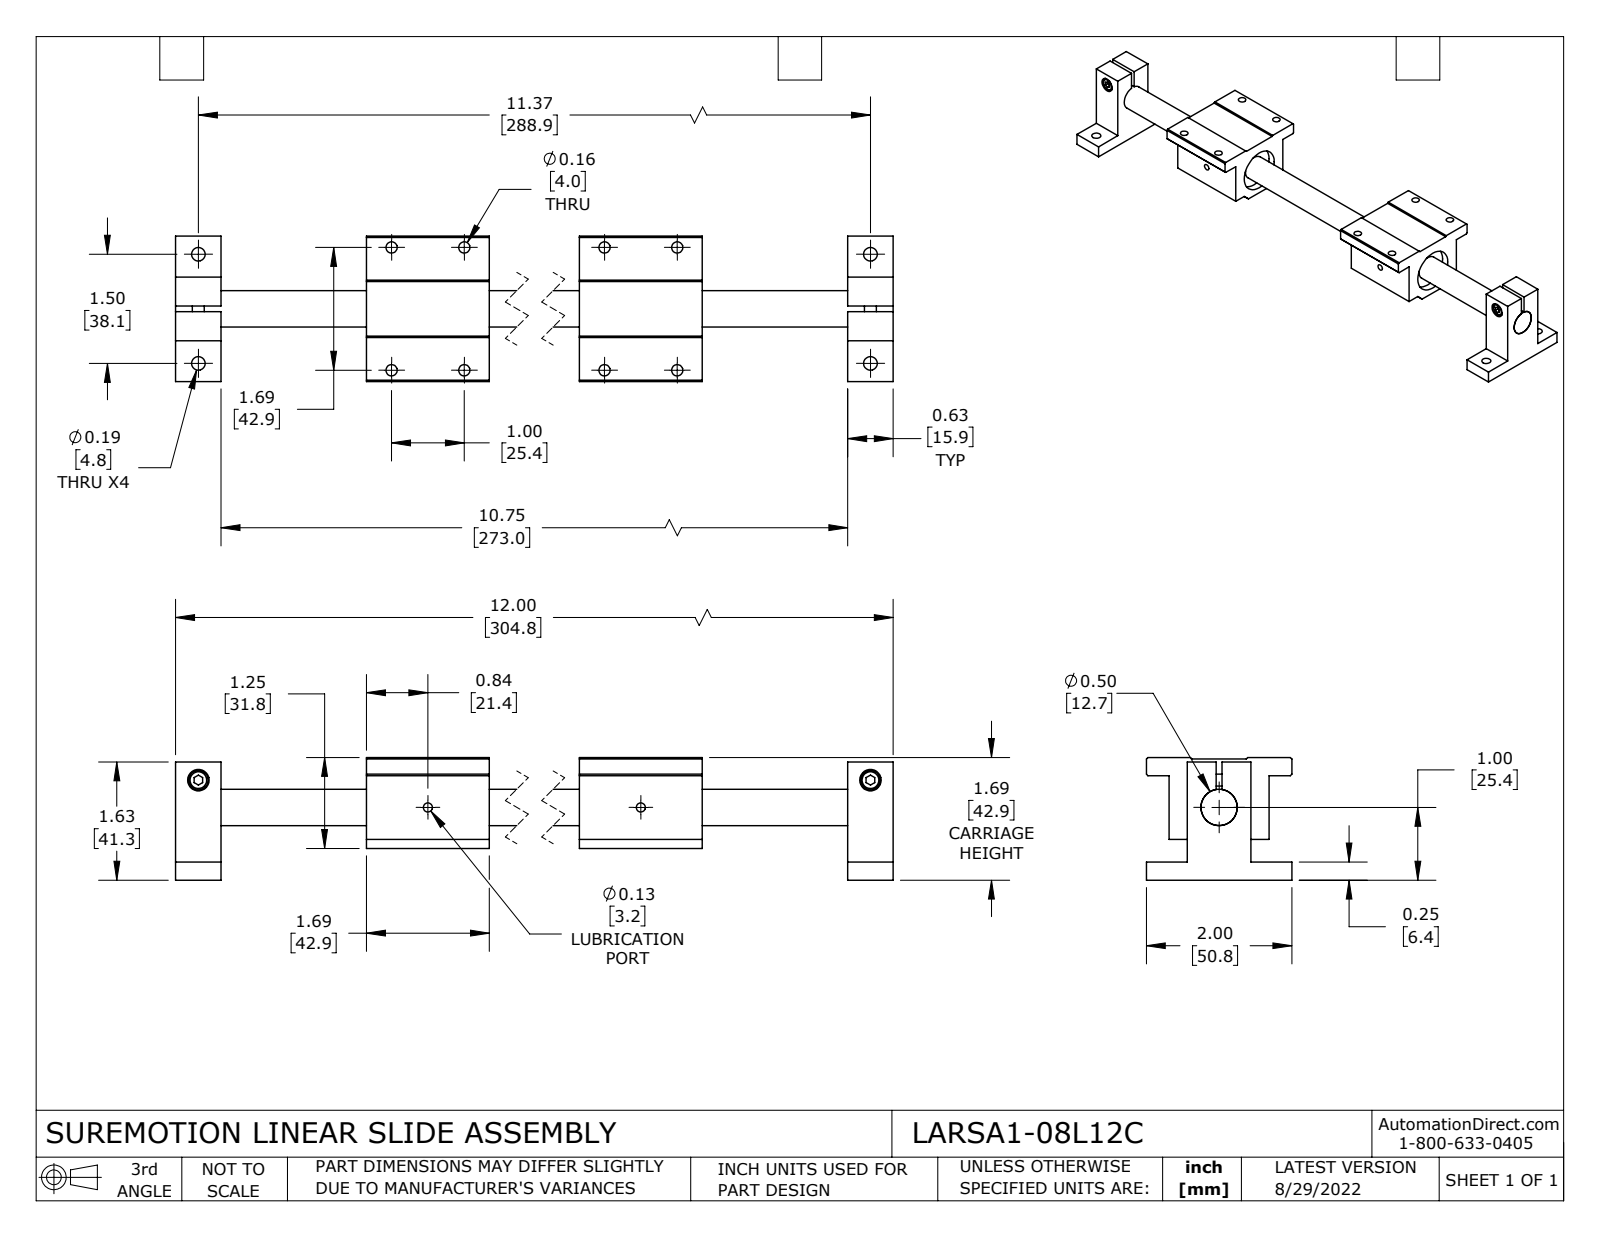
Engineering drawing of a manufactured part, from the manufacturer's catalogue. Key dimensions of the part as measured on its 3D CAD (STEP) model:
Part name (STEP PRODUCT): LARSA1-08L12C-RAIL; LARSACC-001; LARSA1-08L12C
STEP written by: SolidWorks 2021 (CONFIG_CONTROL_DESIGN)
Units: inches
Bodies: 7 solids, 160 faces (96 planar, 60 cylindrical, 4 other)
Overall size (bounding box): 12 × 2 × 1.687
Volume: 9.231 in³ · Surface area: 72.82 in²
Round holes (diameter × count): ⌀0.156 ×8, ⌀0.188 ×4, ⌀0.126 ×2, ⌀0.295 ×2, ⌀0.5 ×1, ⌀0.875 ×1
Round bosses / shafts (diameter × count): ⌀0.27 ×2, ⌀0.164 ×2
Main face-to-face distances: 0.25, 1.125, 1.375, 2, 0.875, 5.061, 1.437, 11.375, 0.625, 0.02
Hole centre spacings: 5.061, 1, 1.688, 1.962, 2.658, 3.098, 3.658, 3.989
